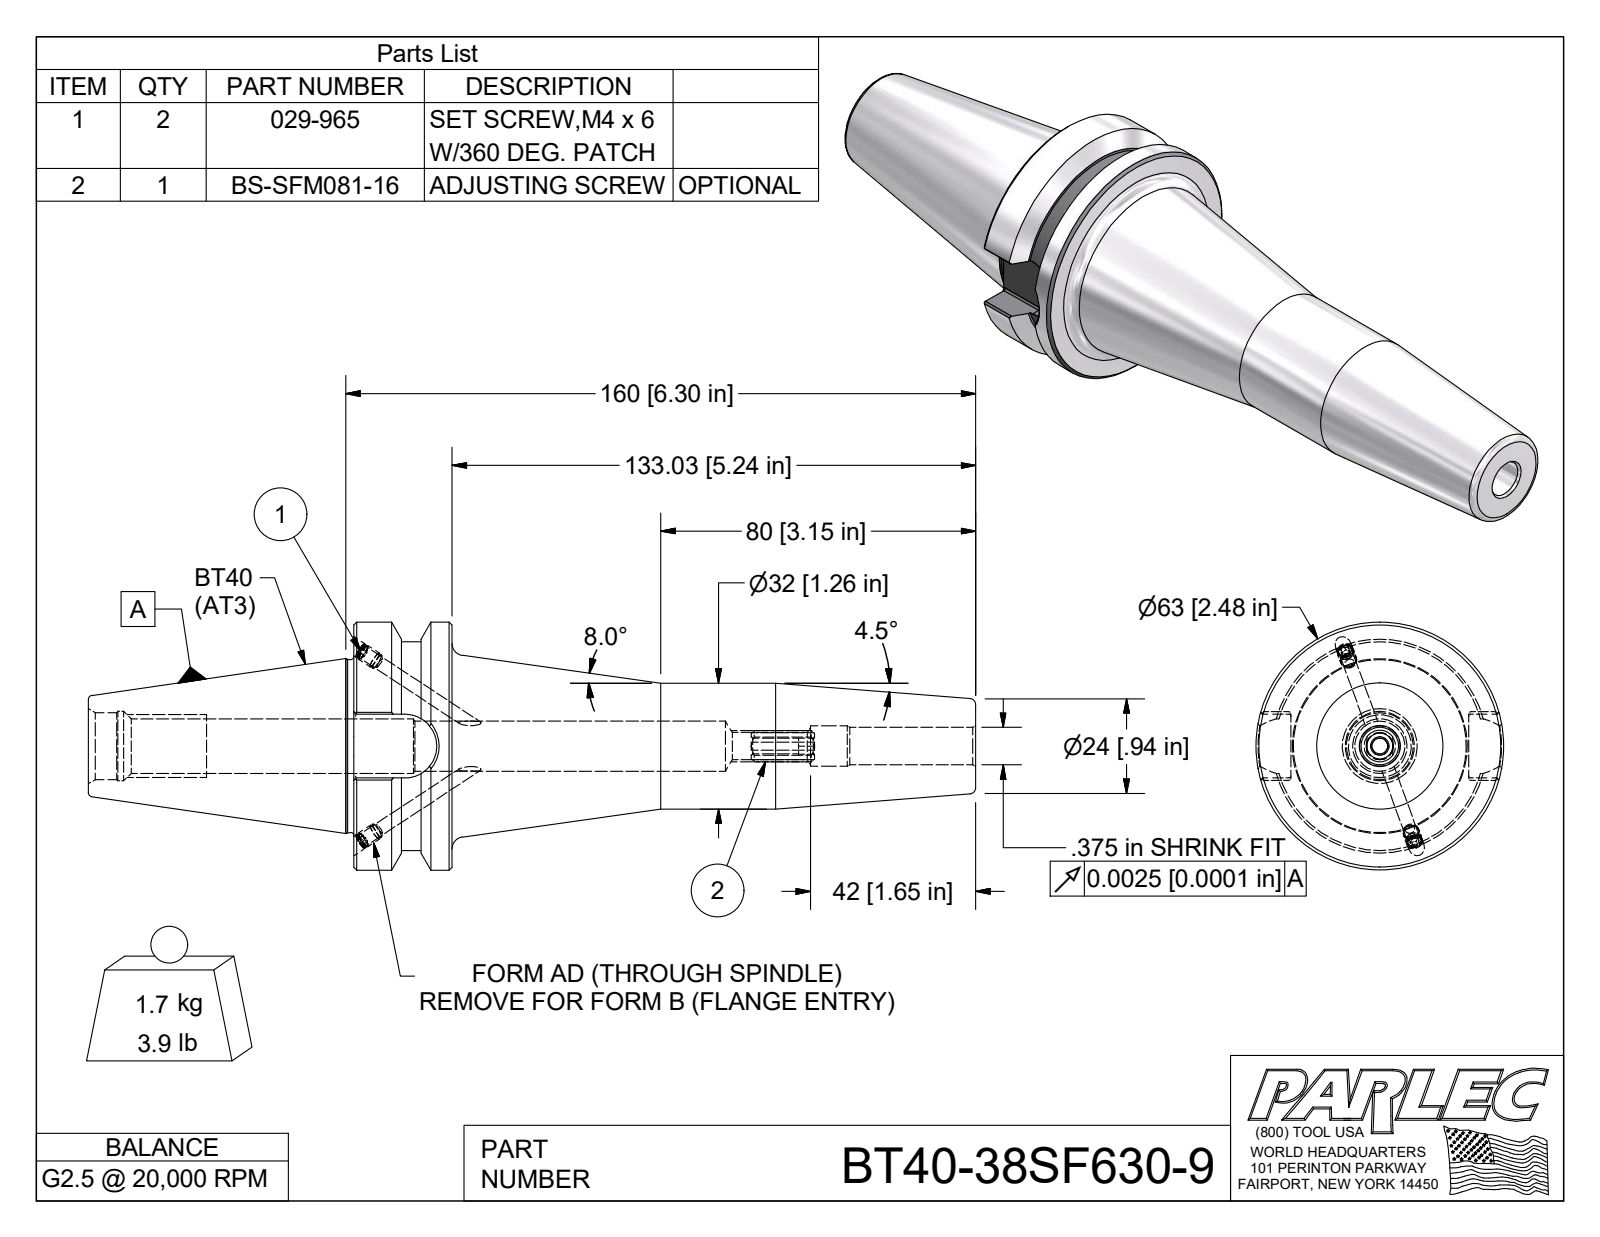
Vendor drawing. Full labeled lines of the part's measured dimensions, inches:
Part name (STEP PRODUCT): BT40-38SF630-9; BT40BC-38SF630-9-1; 029-965; BS-SFM081-16
STEP written by: Autodesk Inventor 2009 (AUTOMOTIVE_DESIGN)
Units: inches
Bodies: 4 solids, 134 faces (57 planar, 33 cylindrical, 44 other)
Overall size (bounding box): 8.874 × 2.48 × 2.48
Volume: 13.89 in³ · Surface area: 63.74 in²
Round holes (diameter × count): ⌀0.13 ×2, ⌀0.161 ×2, ⌀0.374 ×1, ⌀0.404 ×1, ⌀0.694 ×1
Round bosses / shafts (diameter × count): ⌀0.165 ×2, ⌀0.157 ×2, ⌀2.48 ×1, ⌀2.087 ×1, ⌀1.75 ×1, ⌀1.73 ×1, ⌀1.26 ×1
Partial cylindrical surfaces — rounded edges, fillets, slot ends (radius × count): R0.02 ×8, R0.157 ×1, R0.319 ×1
Main face-to-face distances: 0.984, 1.78, 6.221, 5.237, 2.653, 3.637, 8.874, 0.637, 0.762, 1.018
